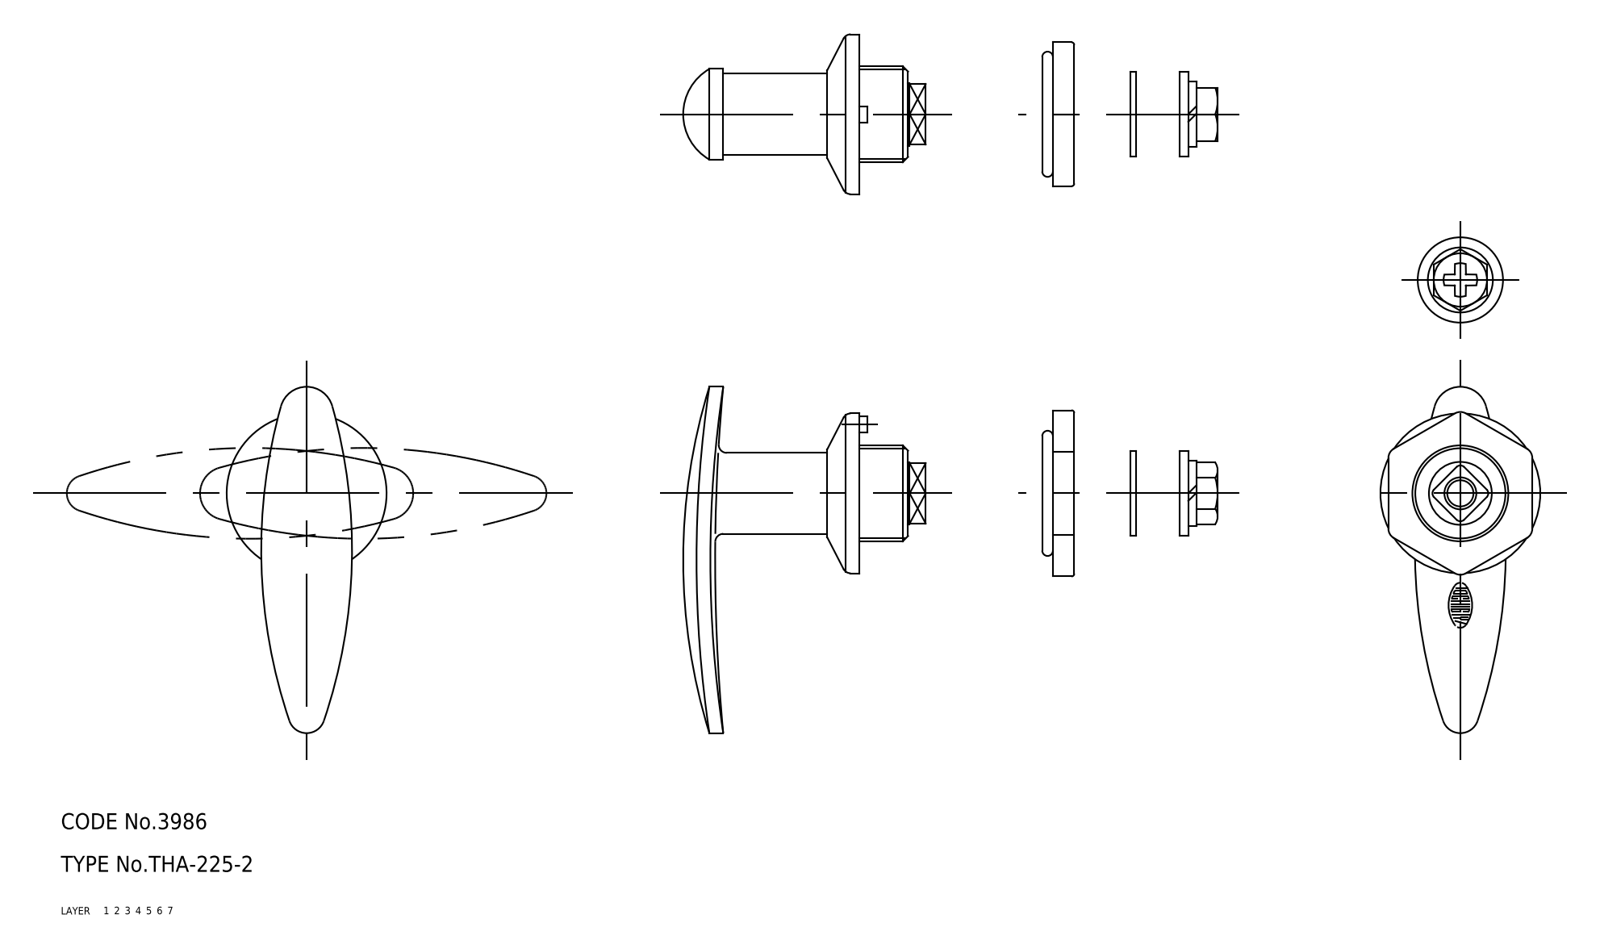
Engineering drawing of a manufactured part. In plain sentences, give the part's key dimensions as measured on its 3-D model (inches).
The part is named "washer_B; washer_A; nut; handle (+3 more)". Its 3-D file was written by "CADfix (AUTOMOTIVE_DESIGN)". It is 6 solids with 142 faces: 0 planar, 0 cylindrical and 142 other. Overall it measures 2.559 by 2.071 by 1.181 inches. Its volume is 0.912 cubic inches and its surface area 15.48 square inches.
